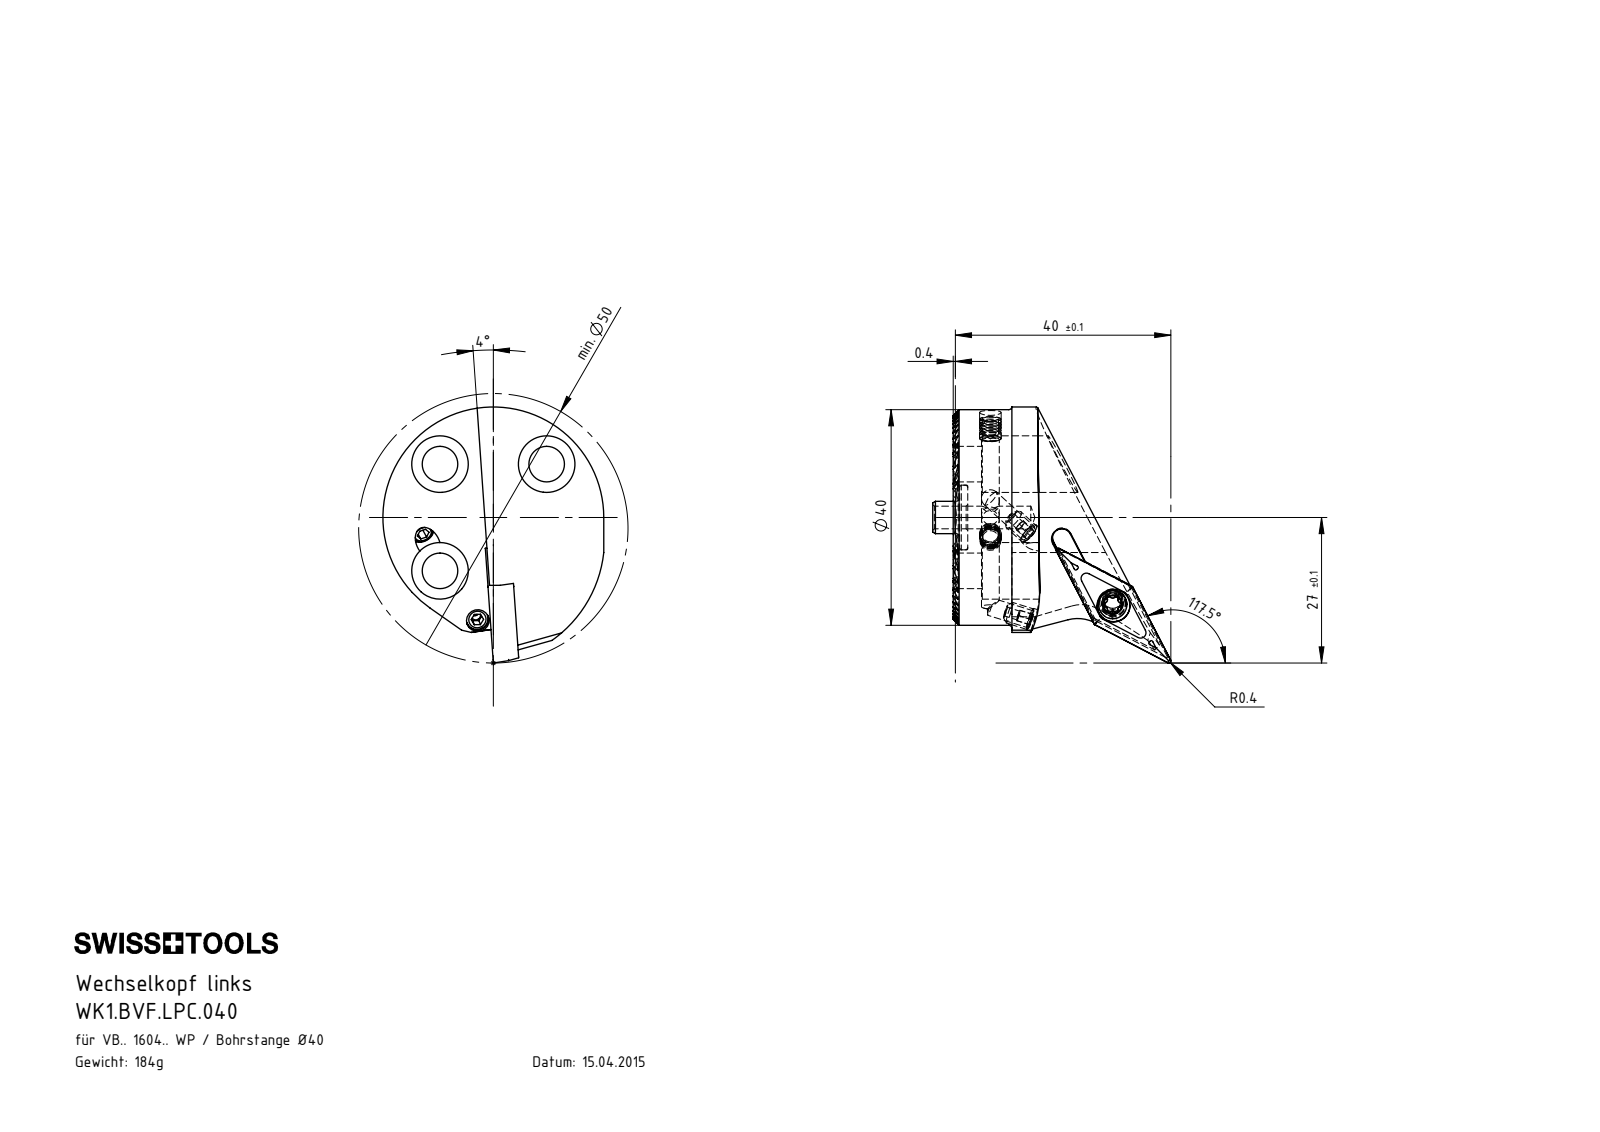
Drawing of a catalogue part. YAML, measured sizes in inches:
part_name: "WK2-ER1.001.012_A_Fertigbearbeitung; VBMT160404; WKX-ER1.004.005_A_PreviewCfg; WCB-ER2.001.009_A (+3 more)"
step_written_by: "SolidWorks 2017 (AUTOMOTIVE_DESIGN)"
units: inches
bodies: {solids: 10, faces: 413, planar: 219, cylindrical: 106, other: 88}
overall_size: [1.87, 1.74, 1.614]
volume: 1.404
surface_area: 16.59
round_holes:
  - {diameter: 0.13, count: 5}
  - {diameter: 0.165, count: 3}
  - {diameter: 0.26, count: 3}
  - {diameter: 0.413, count: 3}
  - {diameter: 0.067, count: 2}
  - {diameter: 0.118, count: 2}
  - {diameter: 0.157, count: 1}
  - {diameter: 0.173, count: 1}
  - {diameter: 0.24, count: 1}
  - {diameter: 0.472, count: 1}
round_bosses_or_shafts:
  - {diameter: 0.157, count: 5}
  - {diameter: 1.575, count: 1}
  - {diameter: 0.236, count: 1}
  - {diameter: 0.207, count: 1}
partial_cylinders:
  - {radius: 0.005, count: 26}
  - {radius: 0.013, count: 6}
  - {radius: 0.023, count: 6}
  - {radius: 0.006, count: 2}
  - {radius: 0.069, count: 1}
  - {radius: 0.276, count: 1}
  - {radius: 0.787, count: 1}
  - {radius: 0.807, count: 1}
face_to_face_distances: [0.051, 0.102, 0.154, 0.511, 0.205, 0.46, 0.358, 0.409, 0.307, 0.256]
hole_center_spacings: [0.551, 0.78, 1.102]
